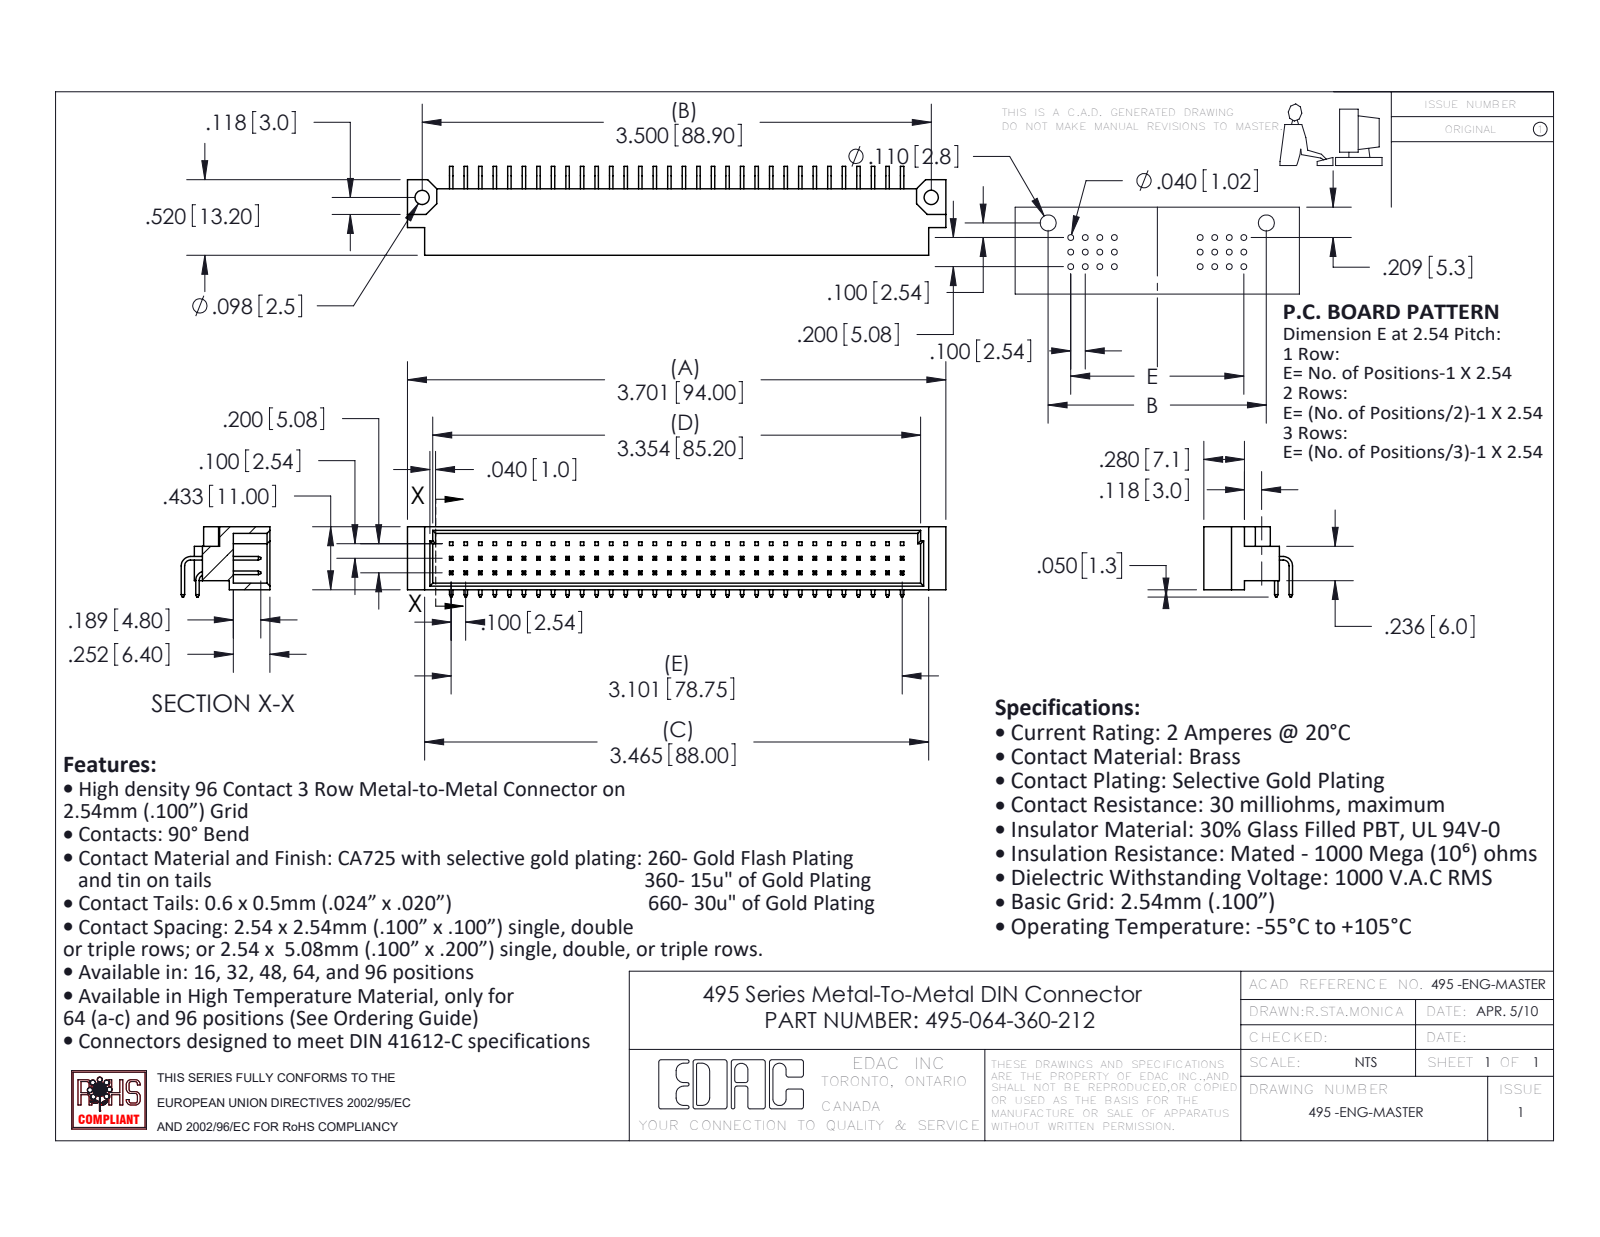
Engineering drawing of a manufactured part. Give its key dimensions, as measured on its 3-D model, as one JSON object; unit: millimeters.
{"part_name": "495 Part_96; 495-064-360-212; 495-290-2; 495-290-3", "step_written_by": "SolidWorks 2020 (AUTOMOTIVE_DESIGN)", "units": "millimeters", "bodies": {"solids": 65, "faces": 1585, "planar": 1453, "cylindrical": 132, "other": 0}, "overall_size": [94, 15.51, 12.27], "volume_mm3": 6330, "surface_area_mm2": 9514, "round_holes": [[2.49, 2]], "partial_cylinders_radius": [[1.02, 2], [1.65, 2]], "face_to_face_distances": [2.54, 5.2, 1.14, 9.86, 0.61, 11, 8.72, 1.6, 9.4, 3.15], "hole_center_spacings": [88.9]}
